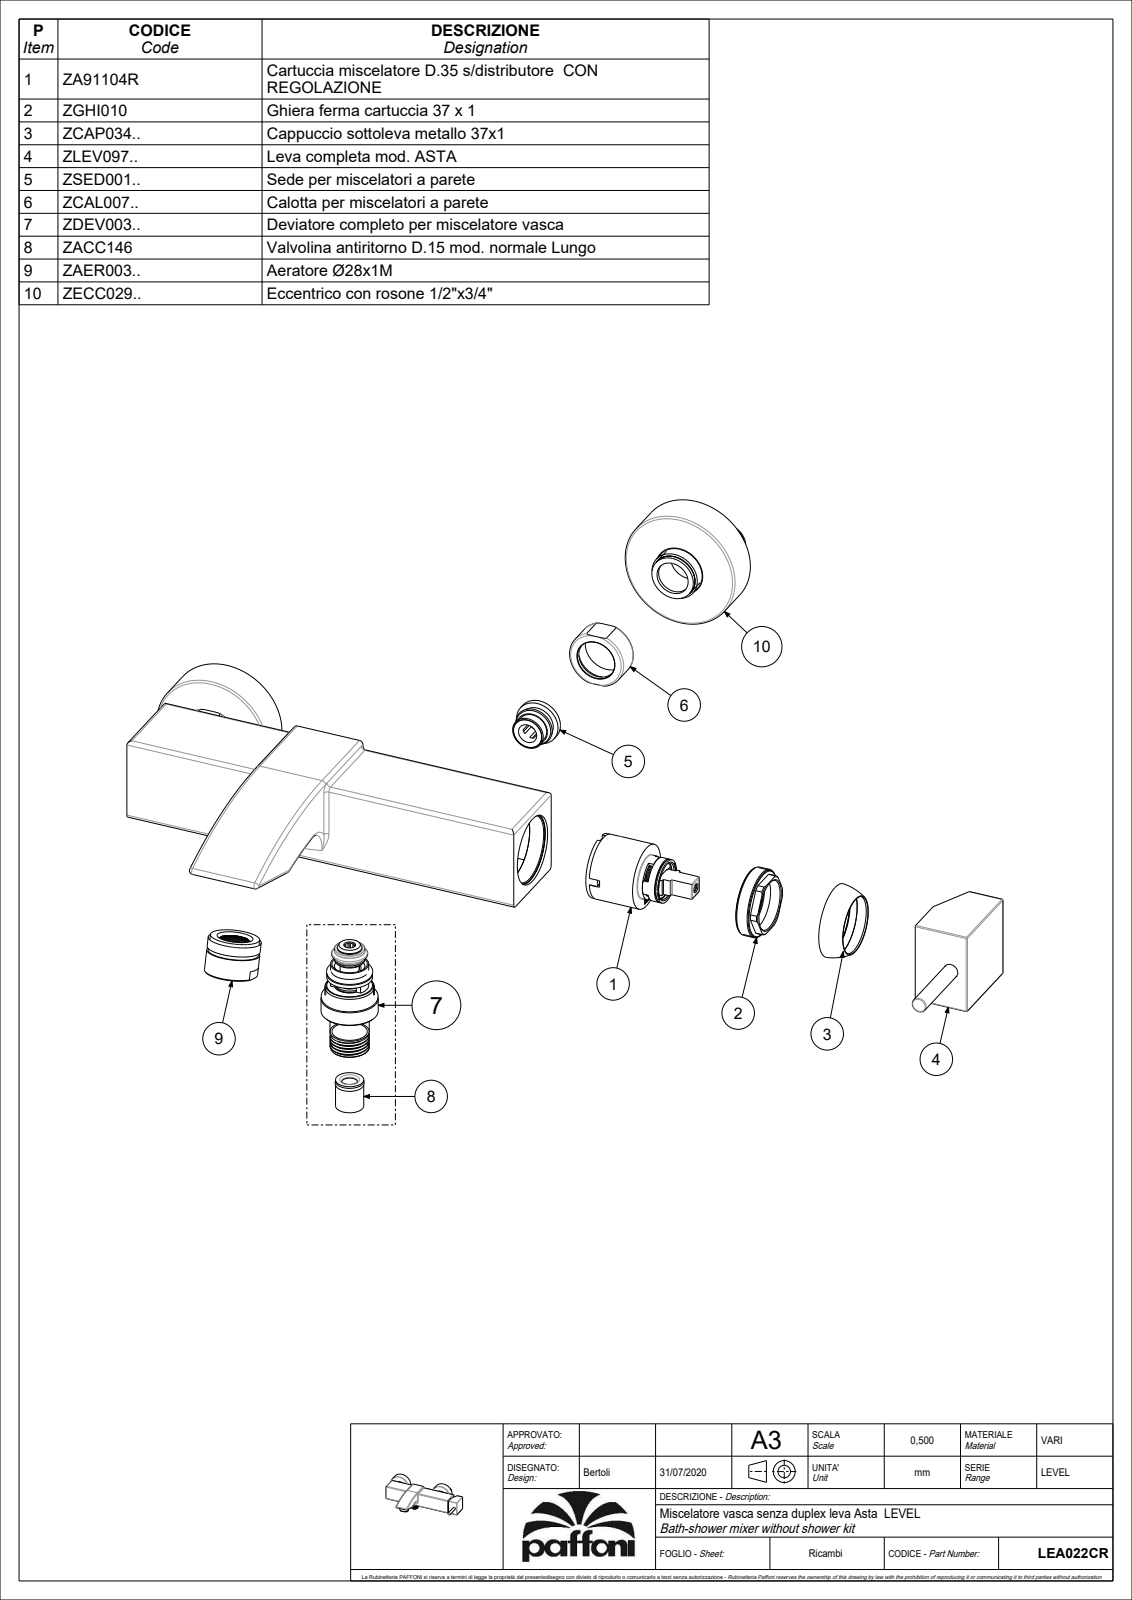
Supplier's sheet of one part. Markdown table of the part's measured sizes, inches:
| quantity | value |
| --- | --- |
| part name | LEA022CR |
| STEP written by | CREO PARAMETRIC BY PTC INC, 2020044 (CONFIG_CONTROL_DESIGN) |
| units | inches |
| bodies | 2 solids, 2926 faces (2262 planar, 393 cylindrical, 271 other) |
| overall size | 10.545 × 6.545 × 2.953 |
| volume | 20.96 in³ |
| surface area | 316.5 in² |
| round holes (diameter × count) | 0.276 × 4, 0.965 × 3, 0.984 × 3, 0.157 × 2, 0.413 × 2, 0.65 × 2, 0.709 × 2, 0.827 × 2, 0.85 × 2, 1.122 × 2, 1.22 × 2, 1.457 × 2 |
| round bosses / shafts (diameter × count) | 1.063 × 3, 0.945 × 3, 2.5 × 2, 1.102 × 2, 1.457 × 1, 1.398 × 1, 1.378 × 1, 1.37 × 1 |
| partial cylindrical surfaces (radius × count) | 0.02 × 37, 0.079 × 15, 0.006 × 11, 0.012 × 4, 0.039 × 2, 0.614 × 2, 0.118 × 1, 0.276 × 1 |
| main face-to-face distances | 0.148, 1.683, 1.831, 1.535, 0.915, 0.768, 0.118, 0.591, 0.738, 2.421 |
| hole center spacings | 0.278, 0.339, 0.449, 0.157, 0.236, 0.394, 0.551, 0.575 |
